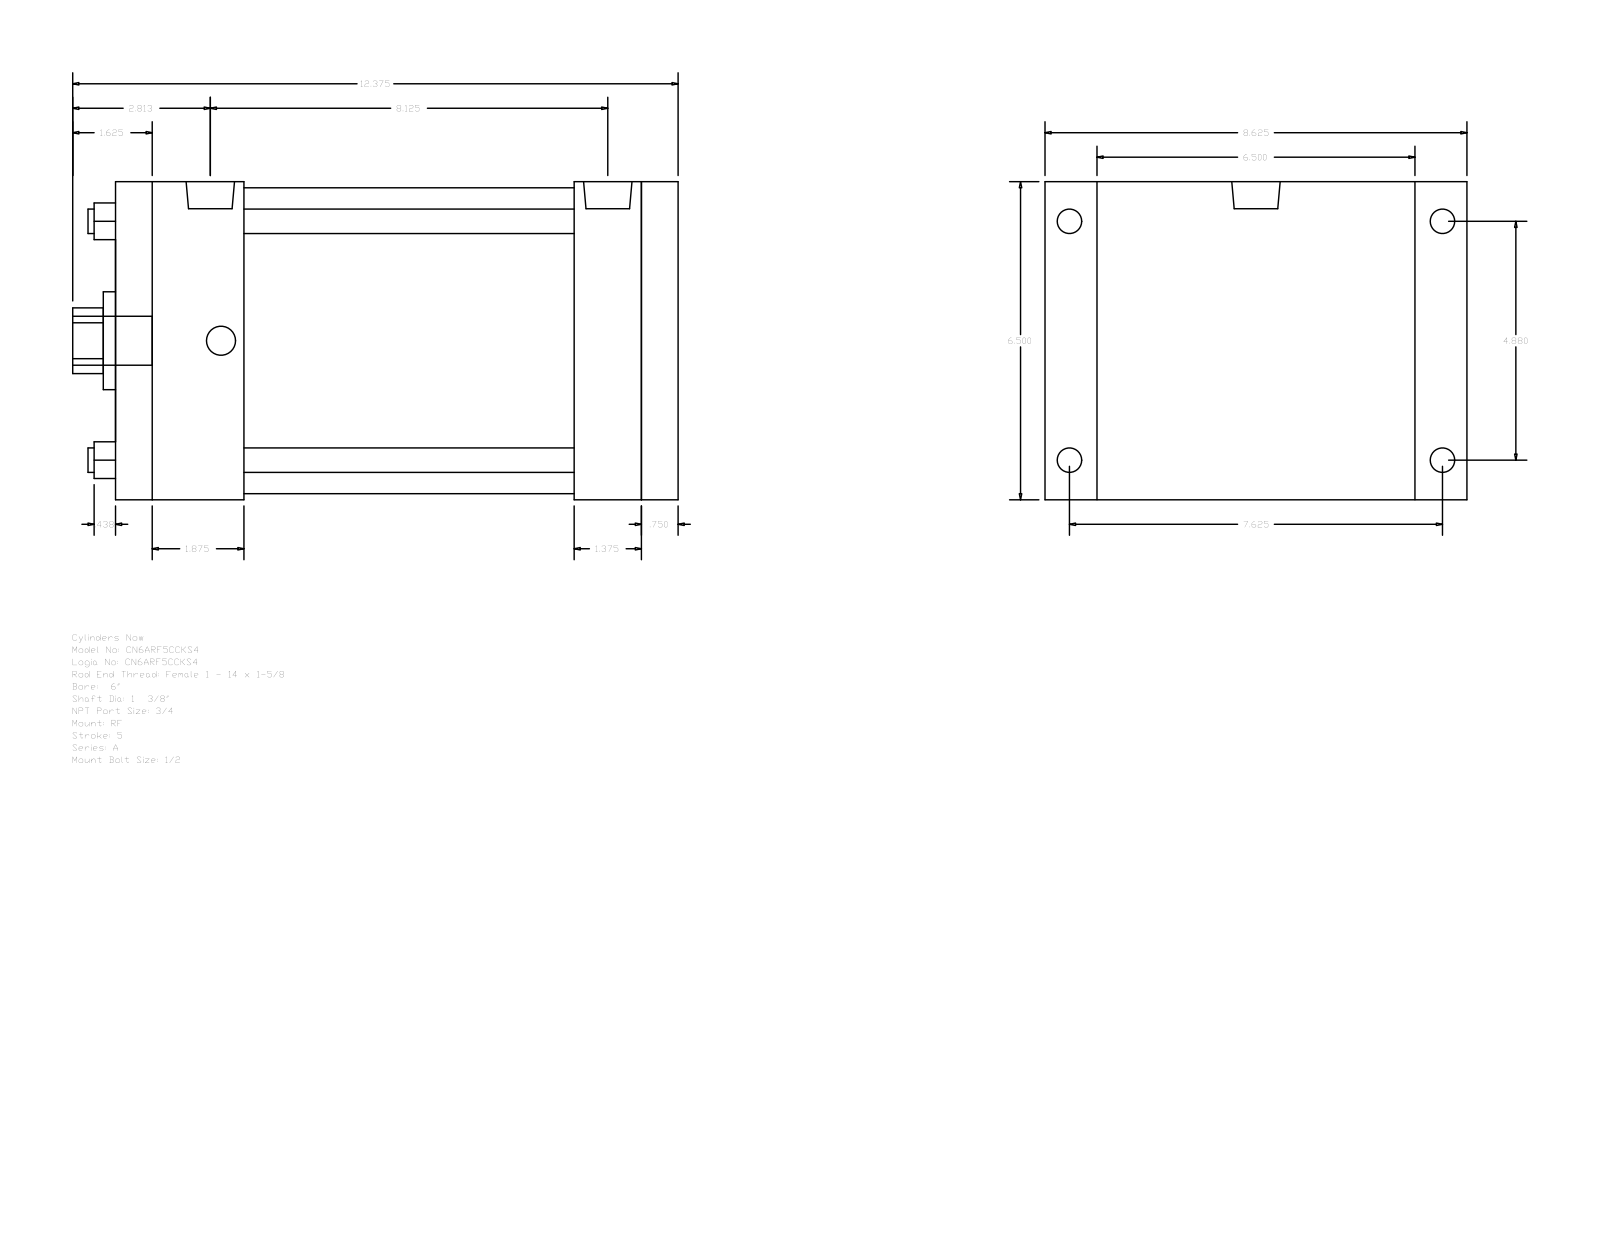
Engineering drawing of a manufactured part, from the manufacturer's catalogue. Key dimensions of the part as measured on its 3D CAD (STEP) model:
Part name (STEP PRODUCT): A_RF__0600_1.375
STEP written by: GSSL Pune (CONFIG_CONTROL_DESIGN)
Units: millimetres
Bodies: 0 solids, 92 faces (64 planar, 28 cylindrical, 0 other)
Overall size (bounding box): 314.32 × 219.07 × 165.1
Round holes (diameter × count): ⌀12.7 ×4, ⌀34.92 ×1, ⌀50.8 ×1, ⌀158.75 ×1
Round bosses / shafts (diameter × count): ⌀15.08 ×4, ⌀12.7 ×4, ⌀25.12 ×2, ⌀25.4 ×1
Partial cylindrical surfaces — rounded edges, fillets, slot ends (radius × count): R17.06 ×1
Main face-to-face distances: 165.1, 292.09, 19.05, 273.04, 66.67, 206.37, 225.42, 238.12, 171.45, 34.92
Hole centre spacings: 87.65, 123.96, 175.31
